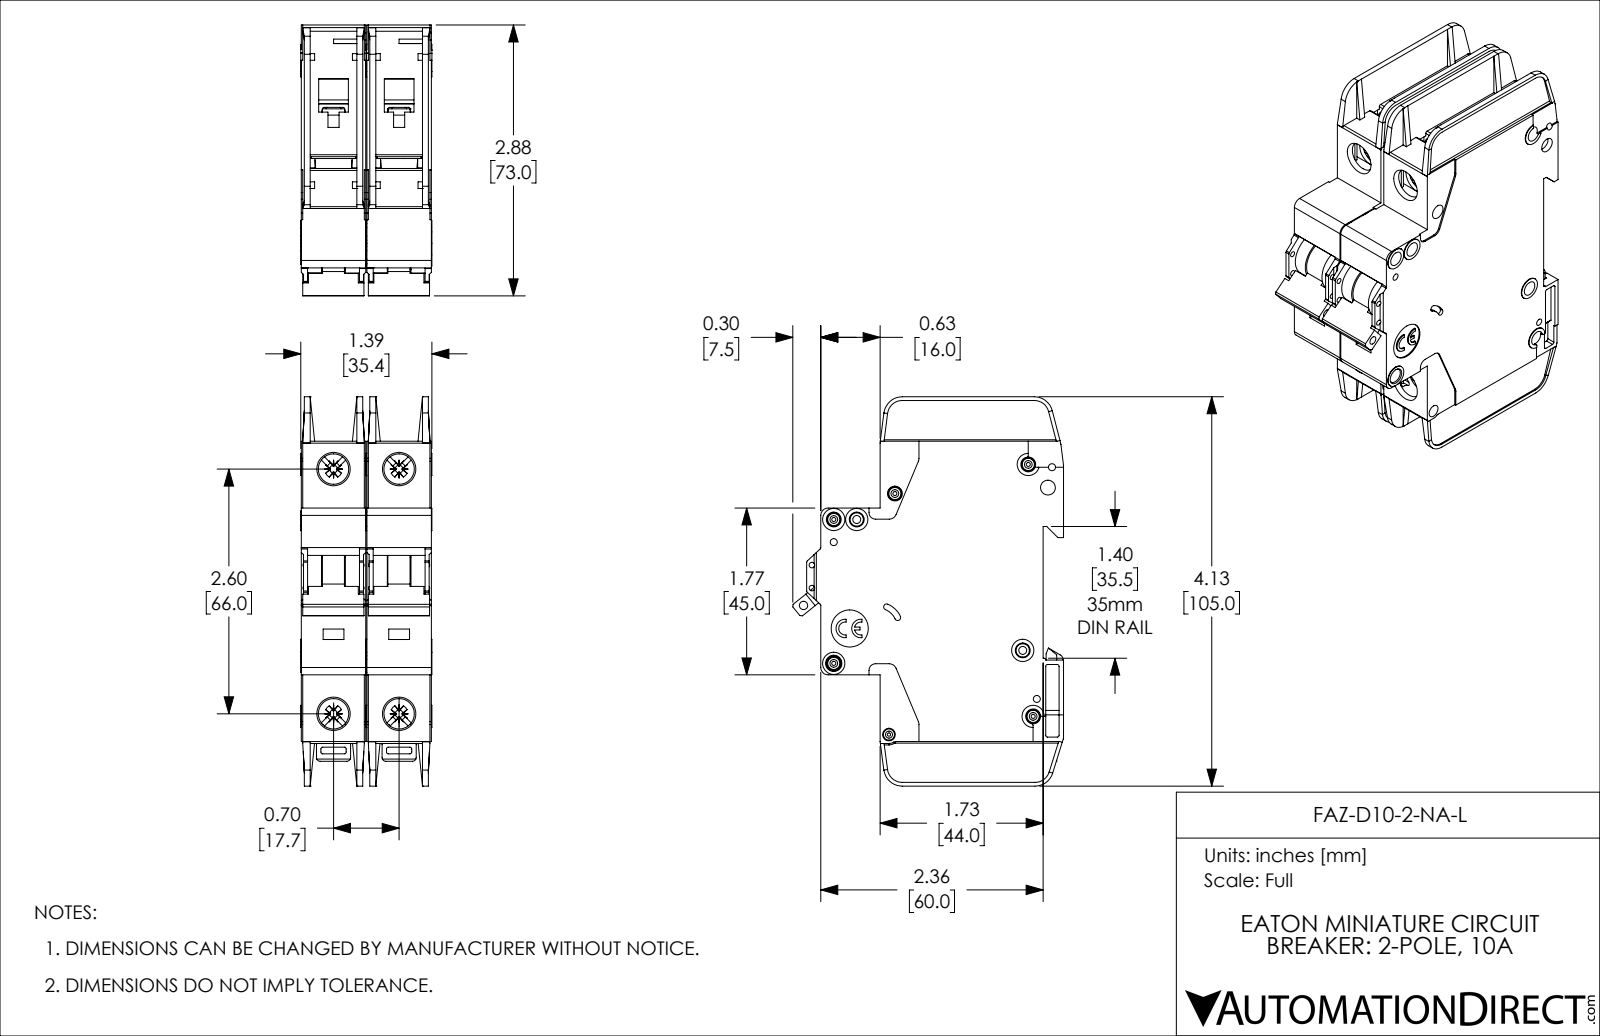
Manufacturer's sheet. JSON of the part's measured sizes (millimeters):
{"part_name": "FAZ-D10-2-NA-L", "step_written_by": "SolidWorks 2019 (AUTOMOTIVE_DESIGN)", "units": "millimeters", "bodies": {"solids": 2, "faces": 2254, "planar": 1342, "cylindrical": 714, "other": 198}, "overall_size": [105, 73.1, 35.4], "volume_mm3": 153500, "surface_area_mm2": 52910, "round_holes": [[4, 8], [1.1, 5], [1.9, 4], [8.2, 4], [1.5, 2], [2.2, 2], [0.9, 1], [2.3, 1], [2.5, 1], [3.4, 1], [10, 1]], "round_bosses_or_shafts": [[3.3, 5], [6, 4], [3, 3], [2.5, 2]], "partial_cylinders_radius": [[0.5, 57], [0.4, 20], [1, 14], [2, 10], [1.1, 8], [0.2, 5], [5, 5], [0.3, 4]], "face_to_face_distances": [17.7, 1.2, 17.4, 15, 2.4, 16.2, 13.8, 35.1, 18.9, 16.5], "hole_center_spacings": [6.2, 13.6, 17.7, 22.1, 66, 68.3, 4.8, 5.1]}
